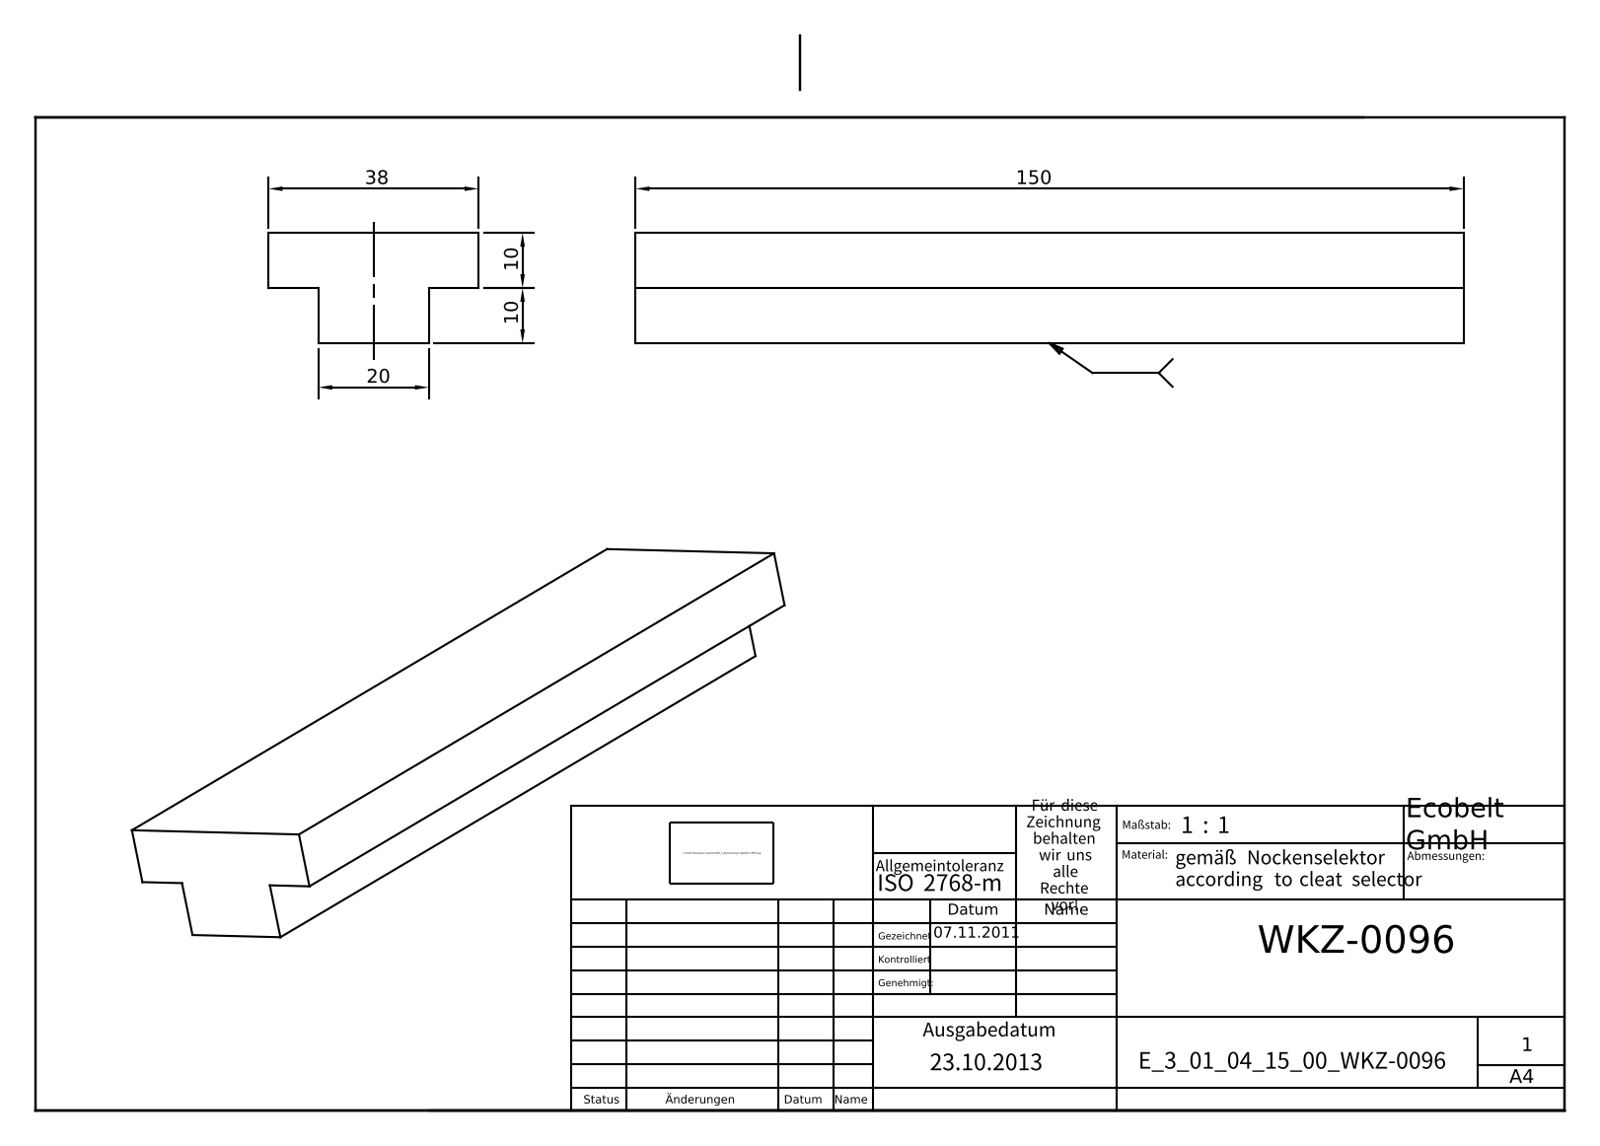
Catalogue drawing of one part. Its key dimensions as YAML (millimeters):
part_name: "E_3_01_04_15_00_WKZ-0096"
step_written_by: "Autodesk Inventor 2025 (AUTOMOTIVE_DESIGN)"
units: millimeters
bodies: {solids: 1, faces: 10, planar: 10, cylindrical: 0, other: 0}
overall_size: [150, 38, 20]
volume: 87000
surface_area: 18560
face_to_face_distances: [10, 20, 9, 29, 38, 150]
